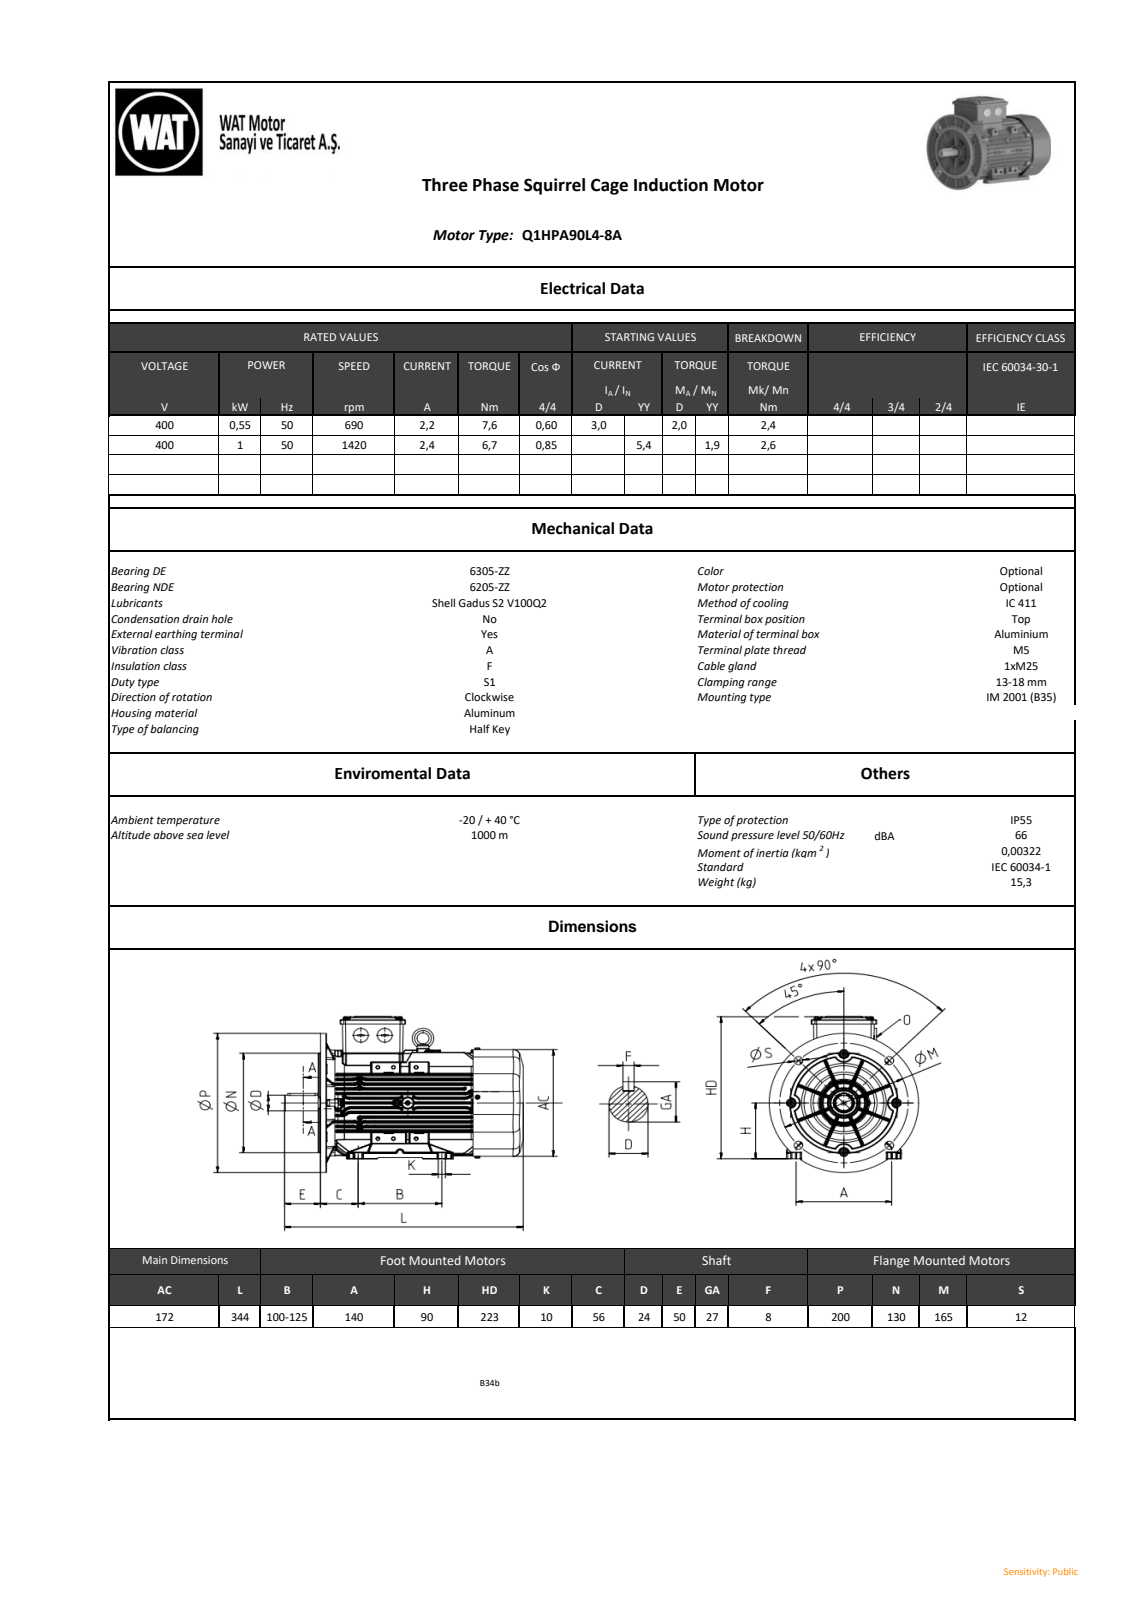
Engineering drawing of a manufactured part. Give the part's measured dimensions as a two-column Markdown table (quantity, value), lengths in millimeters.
| quantity | value |
| --- | --- |
| part name | model1 |
| STEP written by | SIEMENS PLM Software NX2206.8101 (AUTOMOTIVE_DESIGN) |
| units | millimeters |
| bodies | 0 solids, 6359 faces (1488 planar, 2773 cylindrical, 2098 other) |
| overall size | 343.54 × 233.13 × 200 |
| round holes (diameter × count) | 11 × 4, 12 × 4, 9.87 × 1, 37.42 × 1, 79.79 × 1, 97.79 × 1, 115.78 × 1 |
| round bosses / shafts (diameter × count) | 8 × 7, 25 × 3, 5 × 3, 200 × 1, 130 × 1, 102.19 × 1, 84.19 × 1, 27.5 × 1 |
| partial cylindrical surfaces (radius × count) | 1 × 911, 0.8 × 532, 0.98 × 107, 0.5 × 96, 2 × 85, 8 × 28, 1.5 × 20, 4 × 10 |
| main face-to-face distances | 7.5, 91.91, 8.93, 82.98, 23.57, 50.35, 7.37, 90.35, 75.04, 16.87 |
| hole center spacings | 62, 112.27, 149.53, 149.54, 61.99, 62.01, 79.31, 79.47 |
